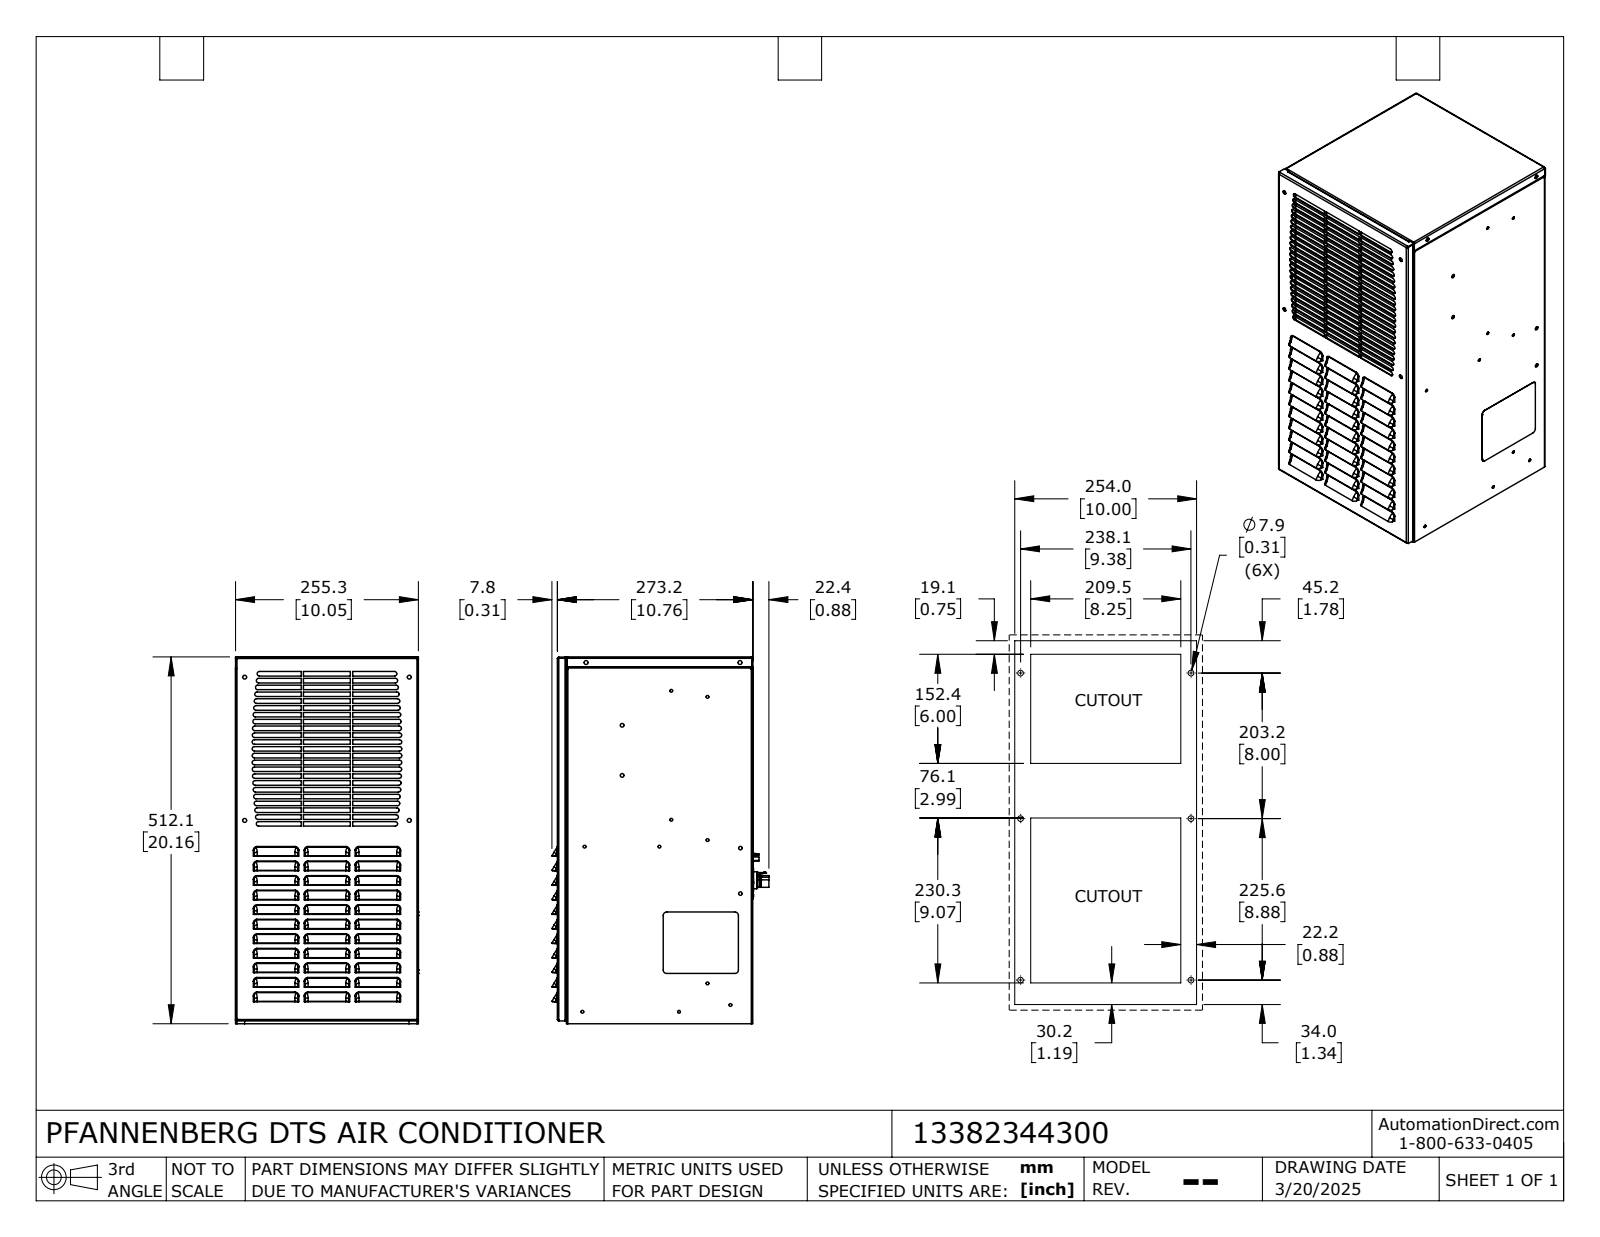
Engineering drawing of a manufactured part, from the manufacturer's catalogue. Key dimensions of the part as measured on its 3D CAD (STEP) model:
Part name (STEP PRODUCT): 13382344300_Default
STEP written by: SolidWorks 2024 (CONFIG_CONTROL_DESIGN)
Units: inches
Bodies: 1 solid, 3066 faces (1574 planar, 955 cylindrical, 537 other)
Overall size (bounding box): 20.16 × 11.943 × 10.059
Volume: 1 997 in³ · Surface area: 1 972 in²
Round holes (diameter × count): ⌀0.217 ×12, ⌀0.156 ×10, ⌀0.187 ×8, ⌀0.213 ×8, ⌀0.071 ×5, ⌀0.142 ×5, ⌀0.169 ×5, ⌀0.209 ×5, ⌀0.149 ×4, ⌀0.281 ×4, ⌀0.313 ×4, ⌀0.203 ×2
Round bosses / shafts (diameter × count): ⌀0.079 ×4, ⌀0.984 ×1
Partial cylindrical surfaces — rounded edges, fillets, slot ends (radius × count): R0.125 ×252, R0.17 ×66, R0.031 ×21, R0.076 ×21, R0.045 ×17, R0.09 ×17, R0.031 ×10, R0.076 ×10
Main face-to-face distances: 0.045, 0.045, 10.05, 10.711, 10.095, 10.622, 0.527, 10.668, 0.572, 0.568
Hole centre spacings: 0.197, 0.294, 4.921, 7.874, 9.195, 0.244, 0.394, 2.5
